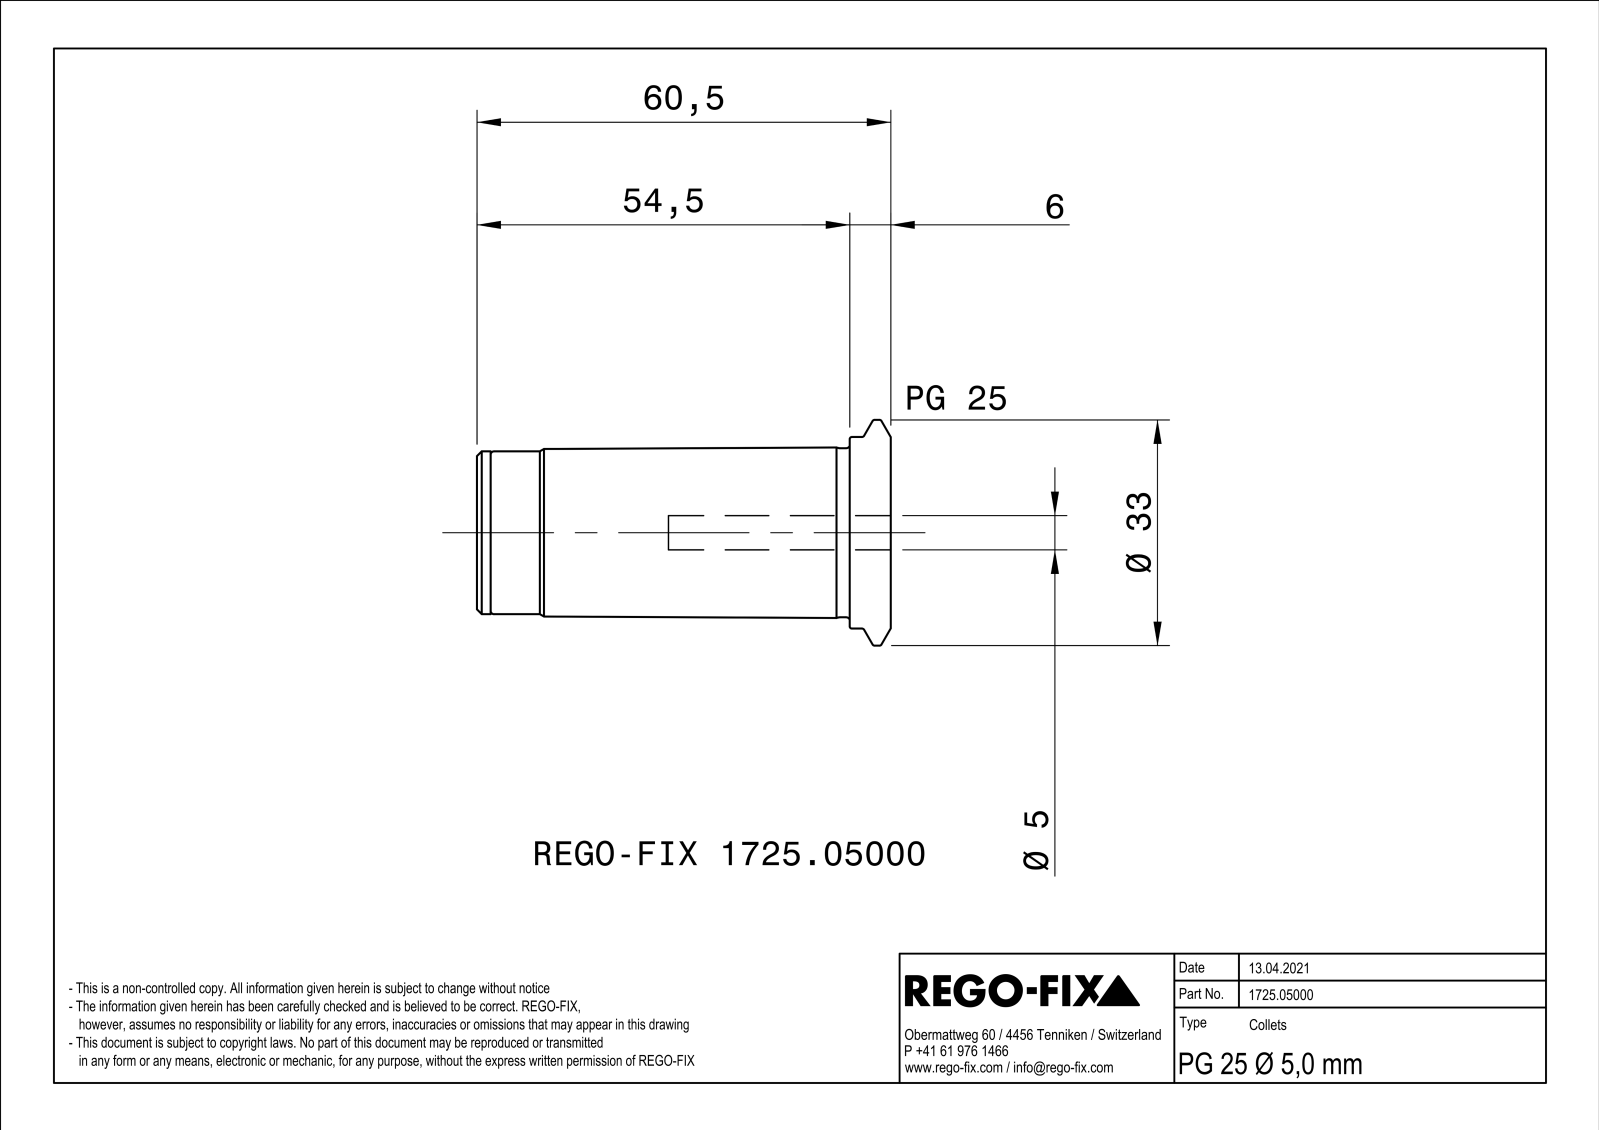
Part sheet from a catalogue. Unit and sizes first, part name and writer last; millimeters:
Units: millimetres
Overall size (bounding box): 60.5 × 33 × 32.99
Round holes (diameter × count): ⌀2.5 ×3, ⌀5 ×1, ⌀5.2 ×1, ⌀6.92 ×1, ⌀8.2 ×1, ⌀9 ×1, ⌀20.4 ×1, ⌀20.92 ×1, ⌀22.2 ×1
Round bosses / shafts (diameter × count): ⌀33 ×1, ⌀28 ×1, ⌀24.7 ×1, ⌀23.8 ×1, ⌀12 ×1
Main face-to-face distances: 1, 60.5, 52.6, 7.9, 58.5, 5.9, 2, 50, 2.6, 8.5
Hole centre spacings: 7.75, 13.43, 13.42
Bodies: 1 solid, 87 faces (23 planar, 24 cylindrical, 40 other)
Part name (STEP PRODUCT): NOCUT
STEP written by: SIEMENS PLM Software Solid Edge ST10 (AUTOMOTIVE_DESIGN)
